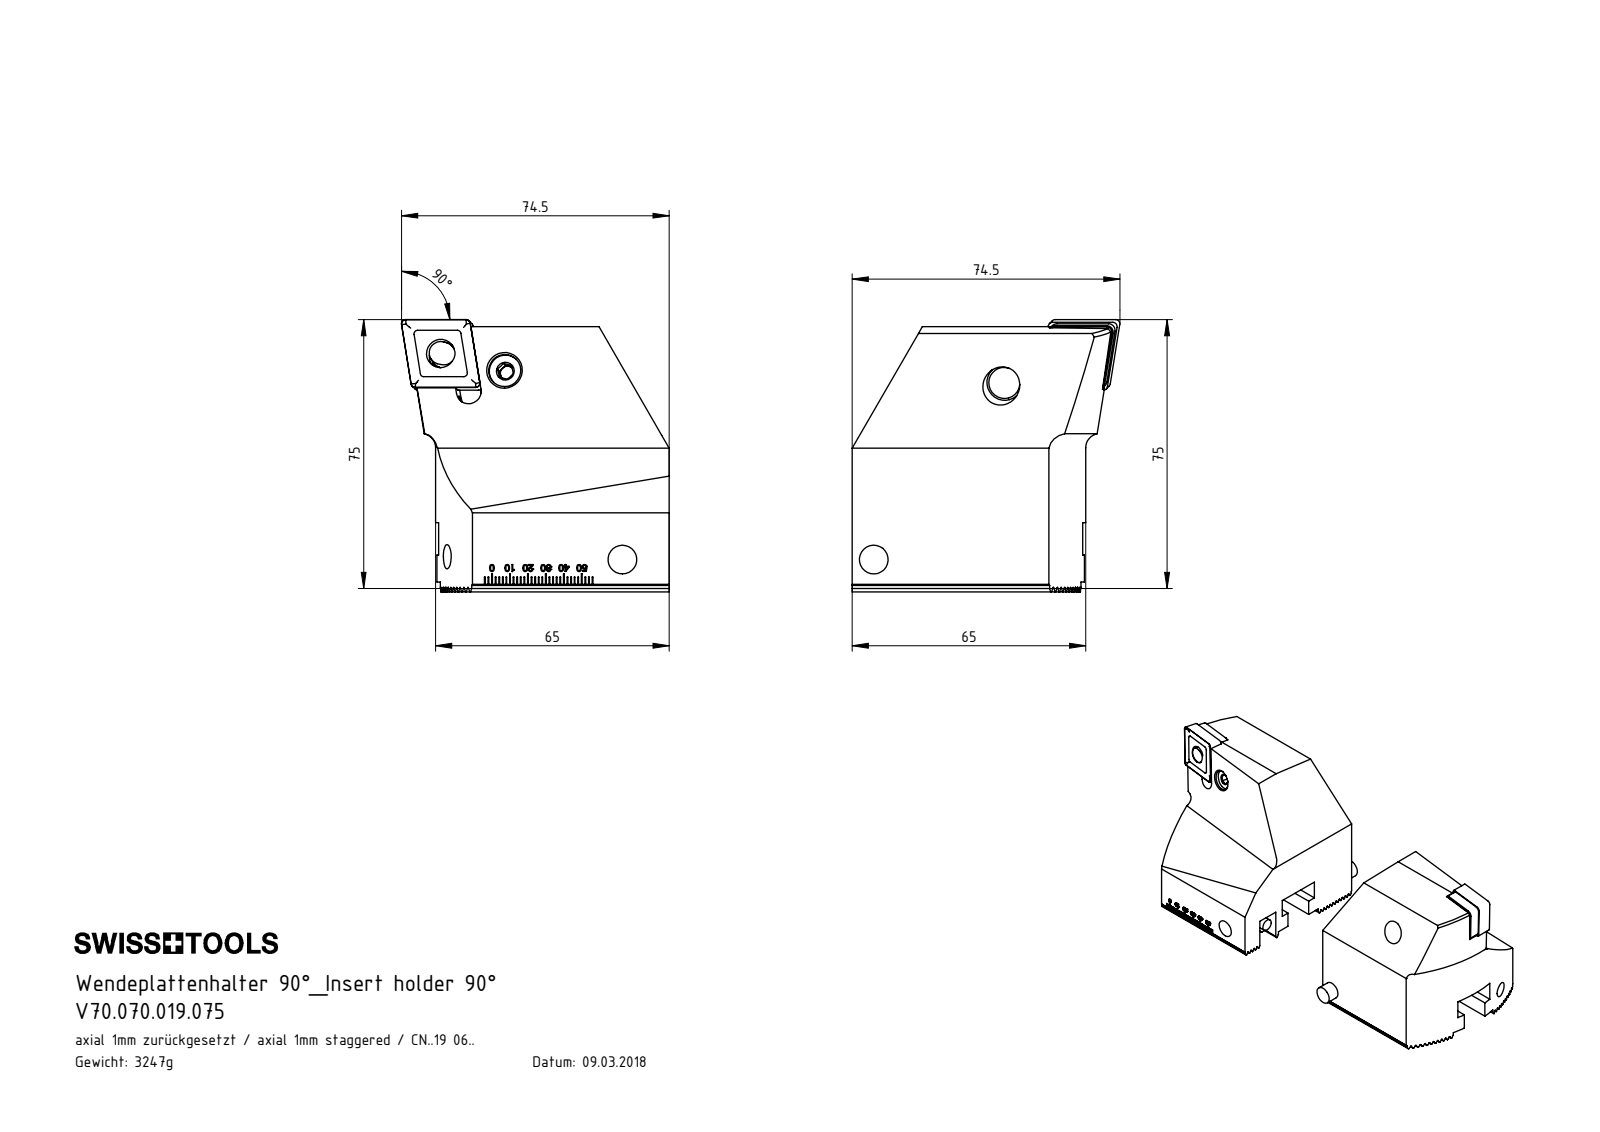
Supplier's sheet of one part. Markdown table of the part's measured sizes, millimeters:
| quantity | value |
| --- | --- |
| part name | WCF-ER4.101.027_A; WCF; WCF-ER3.101.000_A; CNMG190612 (+6 more) |
| STEP written by | SolidWorks 2017 (AUTOMOTIVE_DESIGN) |
| units | millimeters |
| bodies | 8 solids, 600 faces (392 planar, 64 cylindrical, 144 other) |
| overall size | 76.96 × 75.79 × 74.52 |
| volume | 205 922 mm³ |
| surface area | 36 669 mm² |
| round holes (diameter × count) | 8 × 2, 6.8 × 1, 7.94 × 1, 9 × 1, 9.6 × 1, 10.2 × 1 |
| round bosses / shafts (diameter × count) | 10 × 1, 9.9 × 1, 8.6 × 1, 8 × 1, 5.5 × 1, 4.45 × 1 |
| partial cylindrical surfaces (radius × count) | 0.14 × 22, 1.2 × 4, 1.8 × 4, 4.15 × 4, 3.1 × 1, 3.5 × 1, 3.65 × 1, 4 × 1 |
| main face-to-face distances | 1.73, 6.93, 8.66, 3.46, 43.3, 5.2, 41.57, 24.5, 45.5, 10.39 |
| hole center spacings | 0.32, 7, 18.52, 18.81 |
